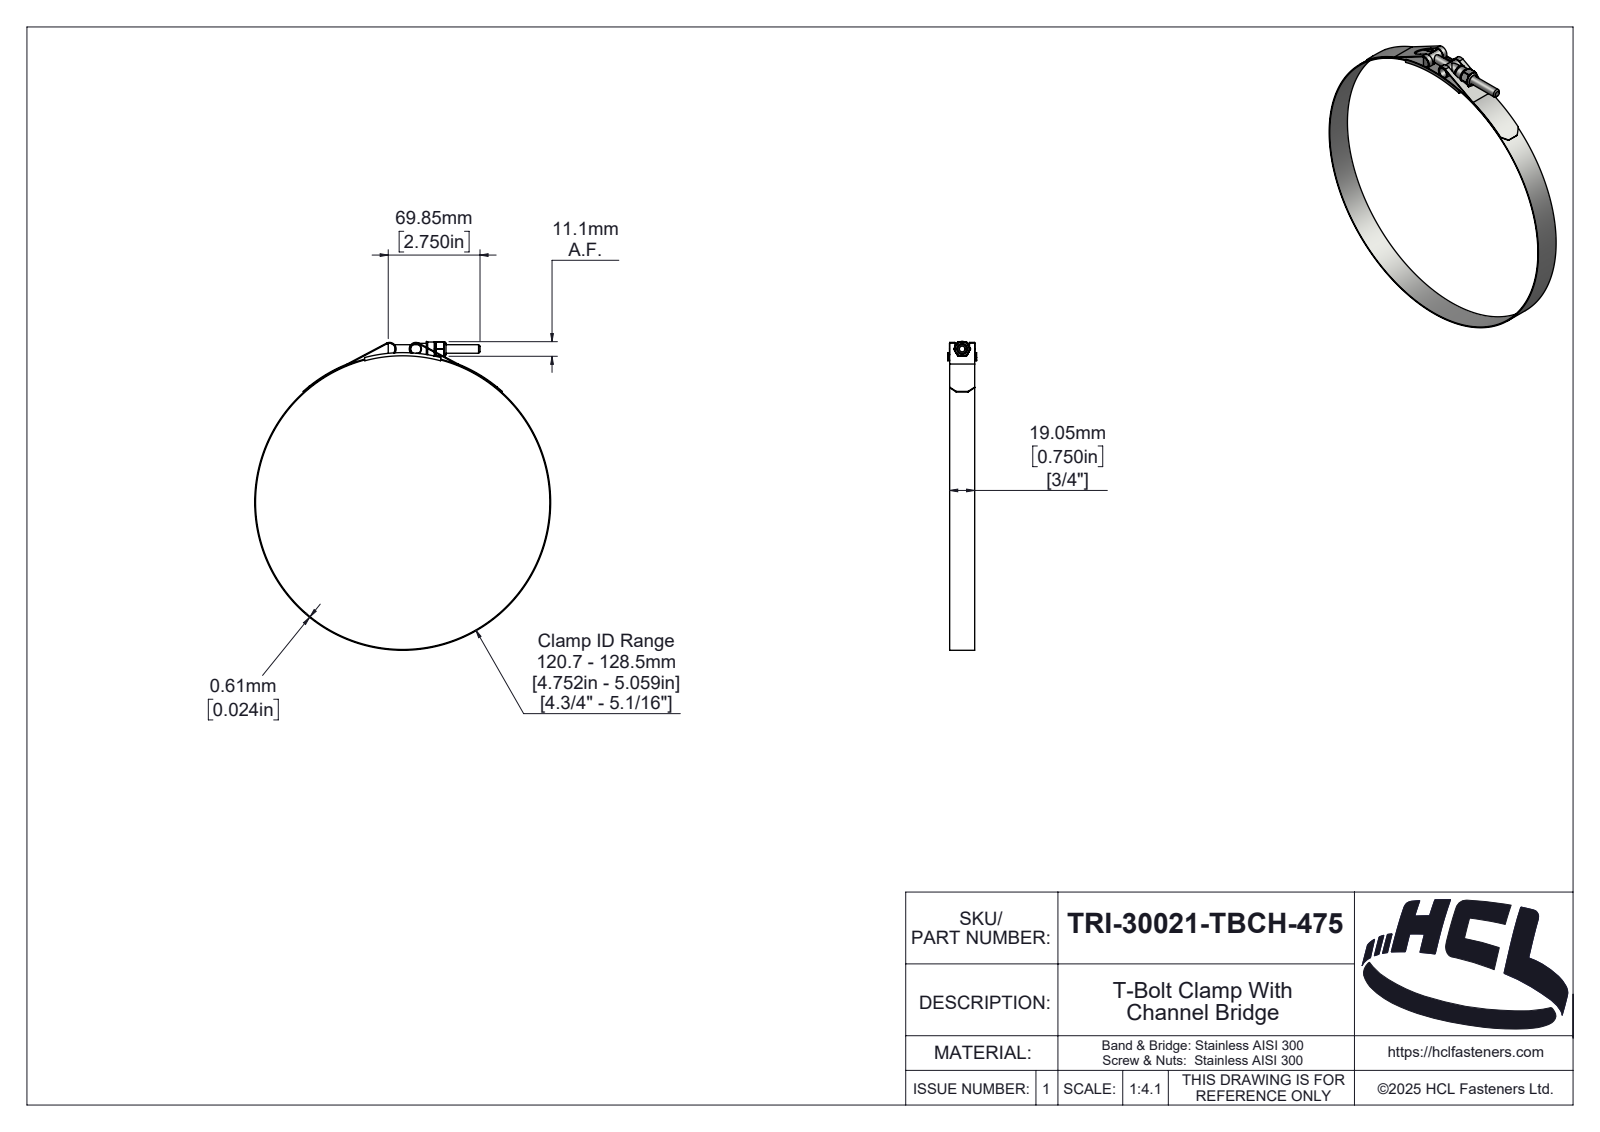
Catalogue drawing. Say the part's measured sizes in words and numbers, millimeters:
The part is named "TRI-30021-TBCH-475". Its 3-D file was written by "SolidWorks 2025 (AUTOMOTIVE_DESIGN)". It is 6 solids with 330 faces: 46 planar, 122 cylindrical and 162 other. Overall it measures 234.9 by 225.22 by 22 millimeters. Its volume is 14 725 cubic millimeters and its surface area 40 167 square millimeters. Round holes: 1 of diameter 5.4, 1 of diameter 6.35, 1 of diameter 6.5, 1 of diameter 7.58, 1 of diameter 224. Round bosses or shafts: 2 of diameter 8.58, 1 of diameter 225.22, 1 of diameter 10.58. Partial cylindrical surfaces (rounded edges, fillets, slot ends): 6 of radius 0.39, 2 of radius 0.5, 2 of radius 4.39, 2 of radius 5, 1 of radius 0.59, 1 of radius 2.42, 1 of radius 3.03, 1 of radius 3.19. The main face-to-face distances are 0.61, 19.06, 1.47, 20.53, 21.39, 0.86, 19.92, 0.74, 22, 11.11. The hole center spacings are 117.
